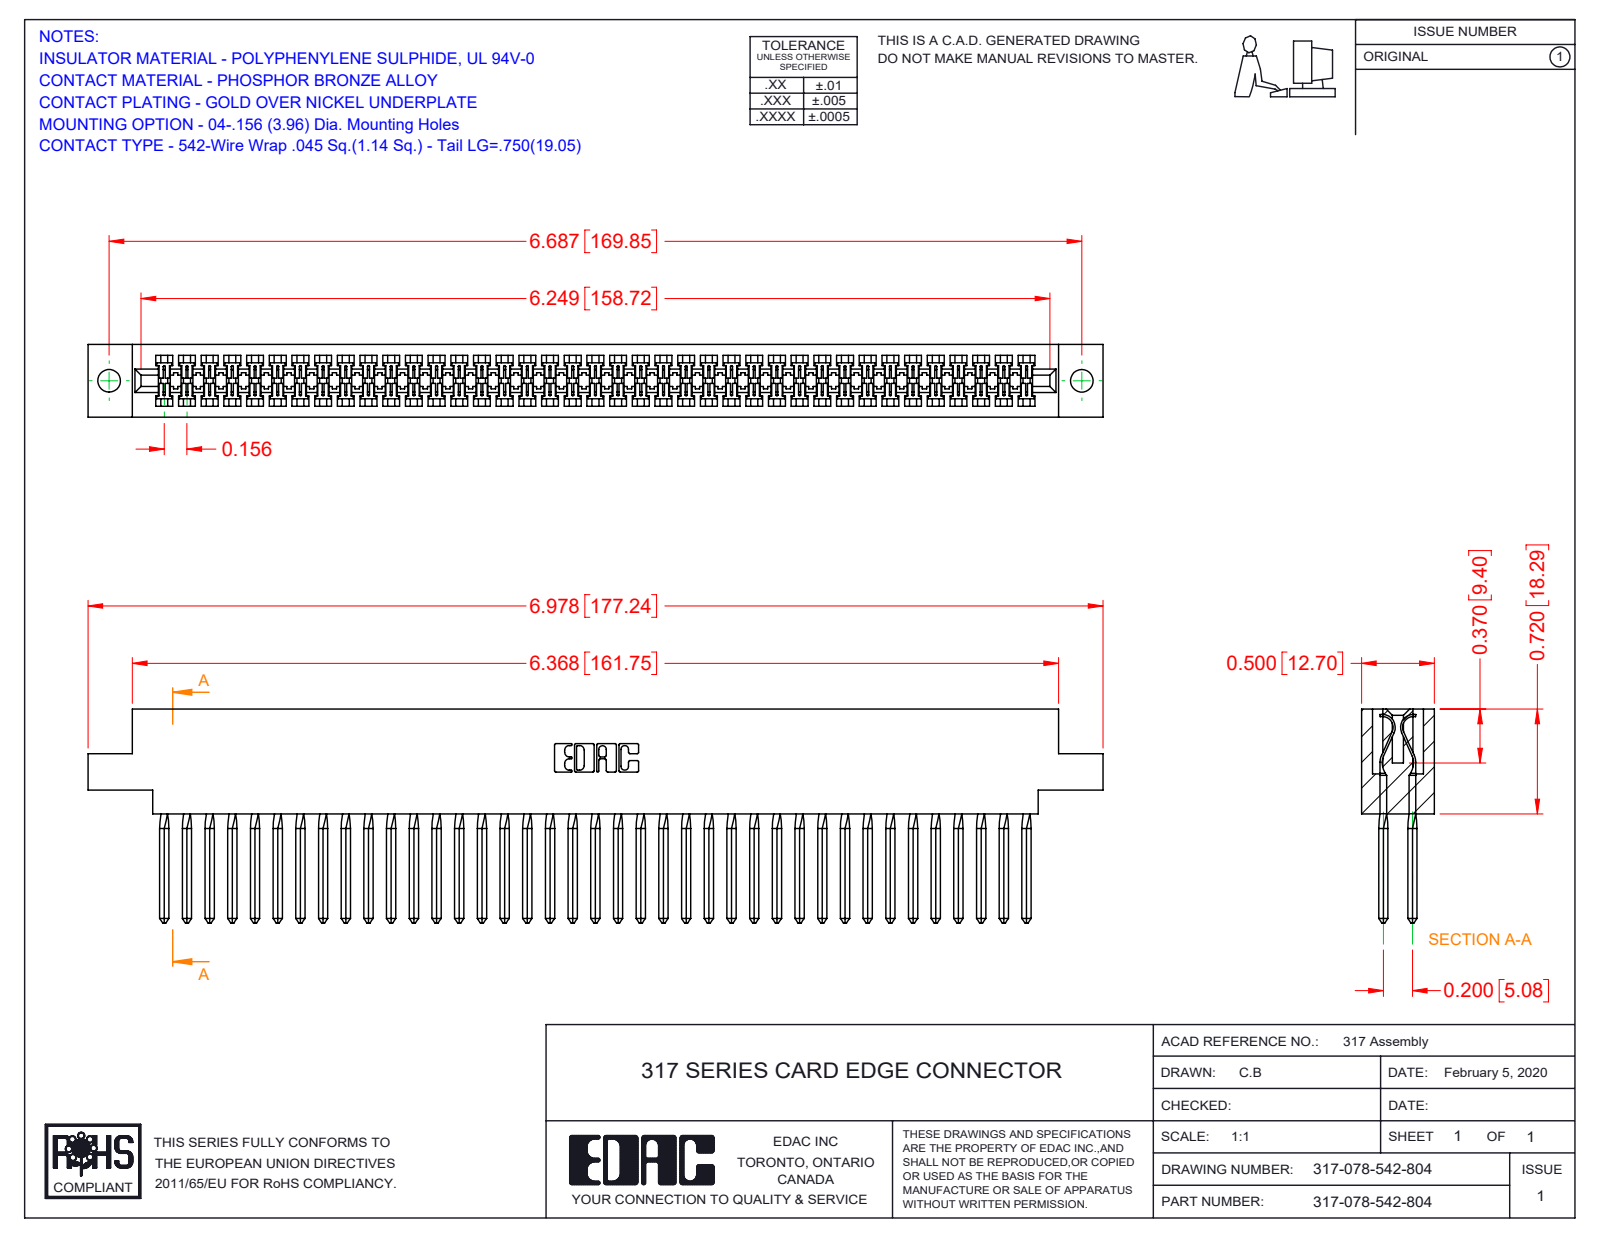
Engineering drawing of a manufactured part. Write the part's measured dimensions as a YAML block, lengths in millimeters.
part_name: "317-078-542-804; 317-290-003_542; 317 Part_.156 Dia - TH"
step_written_by: "SolidWorks 2016 (CONFIG_CONTROL_DESIGN)"
units: millimeters
bodies: {solids: 79, faces: 4548, planar: 3646, cylindrical: 590, other: 312}
overall_size: [177.2, 37.3, 12.7]
volume: 28840
surface_area: 39830
round_holes:
  - {diameter: 4, count: 2}
partial_cylinders:
  - {radius: 0.2, count: 156}
  - {radius: 0.3, count: 22}
  - {radius: 0.2, count: 6}
  - {radius: 0.8, count: 6}
  - {radius: 0.7, count: 3}
  - {radius: 1.9, count: 2}
  - {radius: 2.3, count: 2}
  - {radius: 2.5, count: 2}
face_to_face_distances: [12.7, 1.9, 10.8, 8.9, 5.1, 1.2, 3.3, 9.4, 1.3, 7.5]
hole_center_spacings: [169.8]
